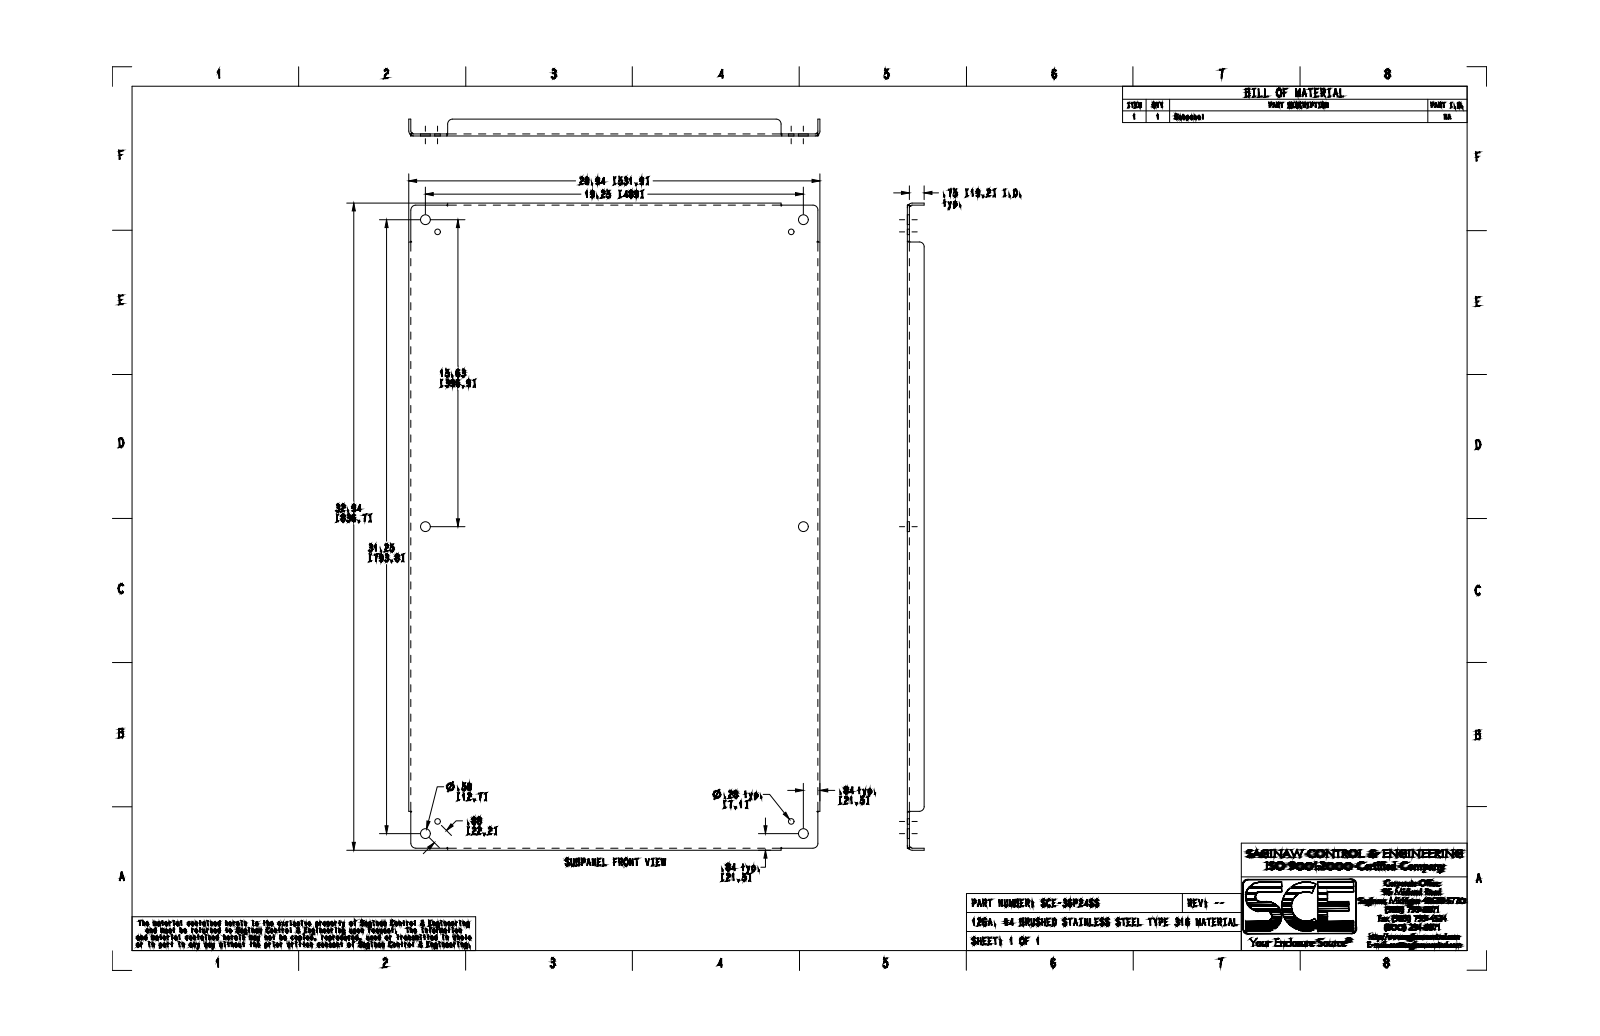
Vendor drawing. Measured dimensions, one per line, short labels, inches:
name: SCE-36P24SS
written by: SolidWorks 2019 (CONFIG_CONTROL_DESIGN)
unit: in
bodies: 1 solid, 84 faces (30 planar, 30 cylindrical, 24 other)
size: 32.941 × 20.941 × 0.858
volume: 77.82 in³; area: 1 510 in²
holes: 6× ⌀0.5, 4× ⌀0.281
rounds: 8× R0.25, 4× R0.246, 2× R0.142, 2× R0.143
face distances: 0.104, 20.838, 32.838, 20.734, 20.942, 32.734, 32.942, 0.754, 0.858, 1.979
hole spacings: 0.875, 15.02, 15.626, 18.643, 23.925, 24.795, 30.639, 35.855
